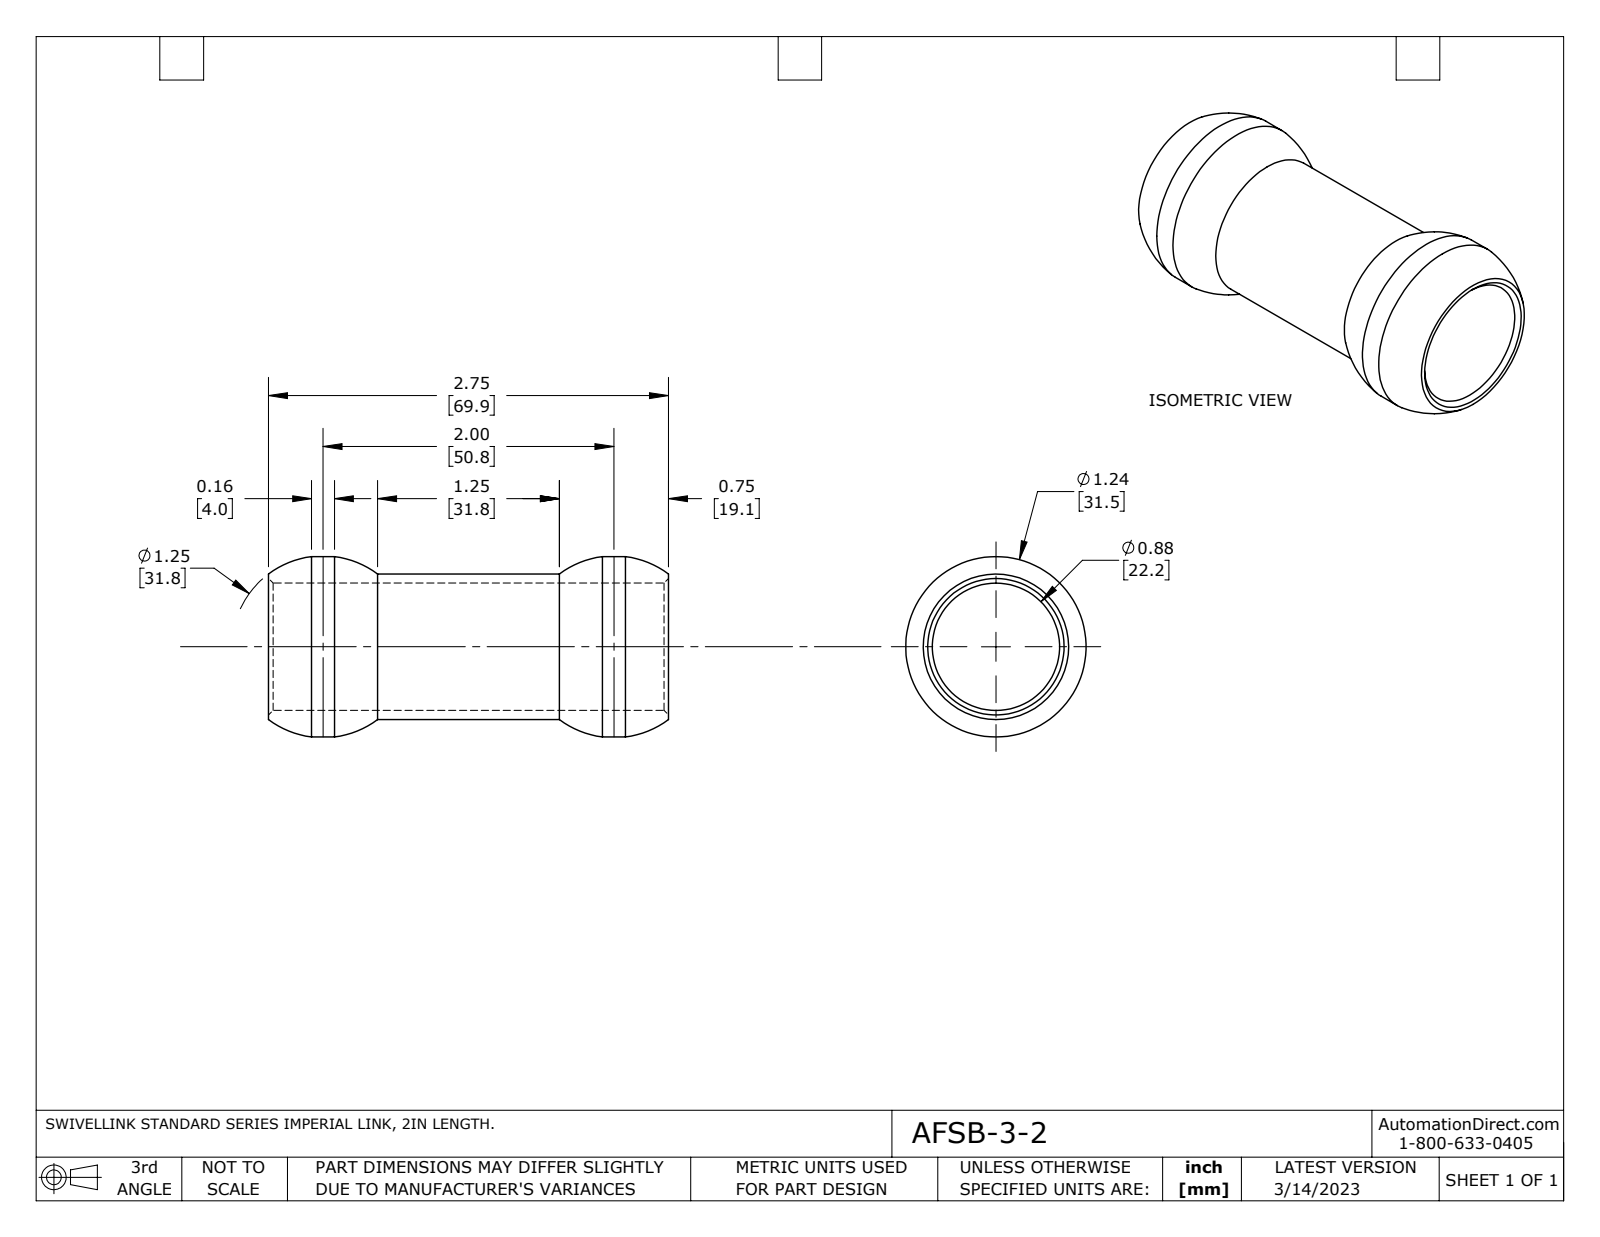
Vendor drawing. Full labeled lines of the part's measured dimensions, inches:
Part name (STEP PRODUCT): AFSB-3-2
STEP written by: SolidWorks 2021 (AUTOMOTIVE_DESIGN)
Units: inches
Bodies: 1 solid, 12 faces (2 planar, 4 cylindrical, 6 other)
Overall size (bounding box): 2.75 × 1.24 × 1.24
Volume: 0.937 in³ · Surface area: 17.61 in²
Round holes (diameter × count): ⌀0.875 ×1
Round bosses / shafts (diameter × count): ⌀1.24 ×1, ⌀1 ×1
Main face-to-face distances: 2.75
